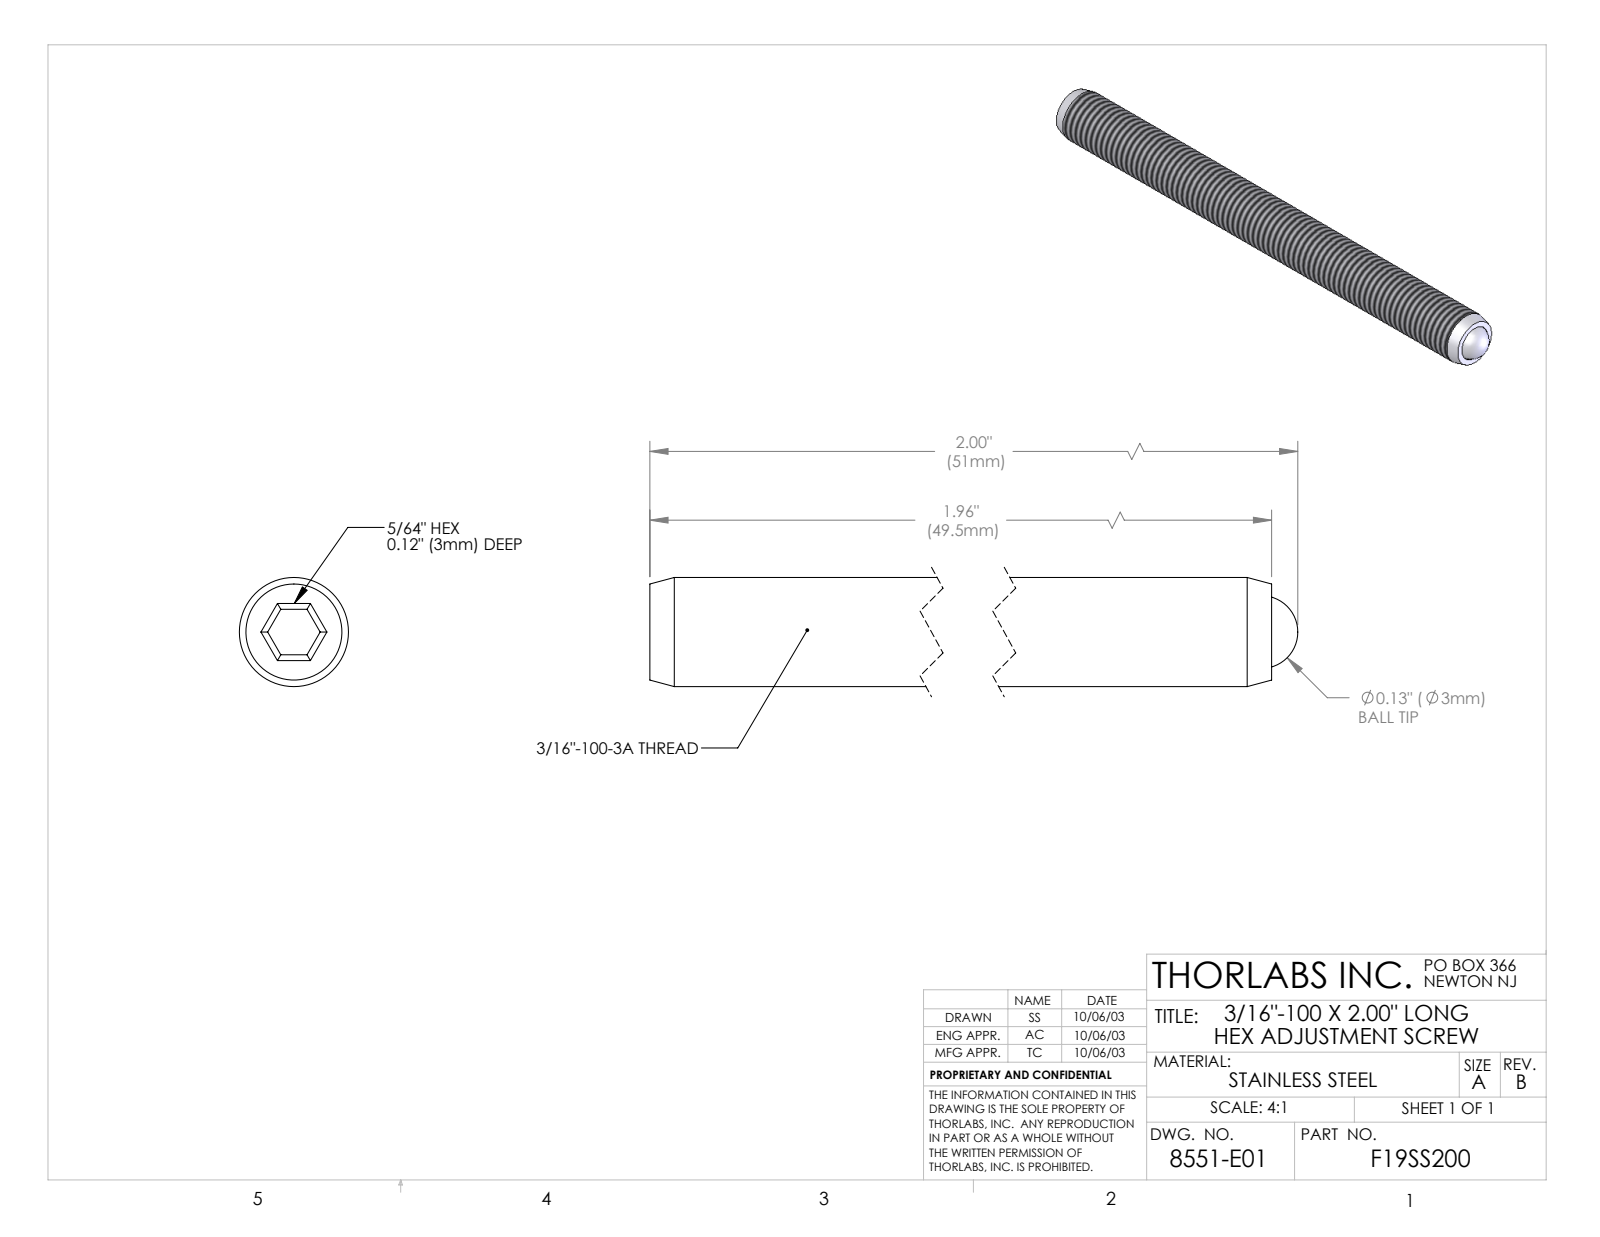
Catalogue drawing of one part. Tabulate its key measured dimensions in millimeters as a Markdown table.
| quantity | value |
| --- | --- |
| part name | 8551-E0W |
| STEP written by | SolidWorks 2007 (AUTOMOTIVE_DESIGN) |
| units | millimeters |
| bodies | 2 solids, 29 faces (15 planar, 4 cylindrical, 10 other) |
| overall size | 50.8 × 4.76 × 4.76 |
| volume | 873 mm³ |
| surface area | 836 mm² |
| round holes (diameter × count) | 3.19 × 1 |
| round bosses / shafts (diameter × count) | 4.76 × 1 |
| main face-to-face distances | 1.98, 49.66, 3.05, 46.61, 1.99 |
